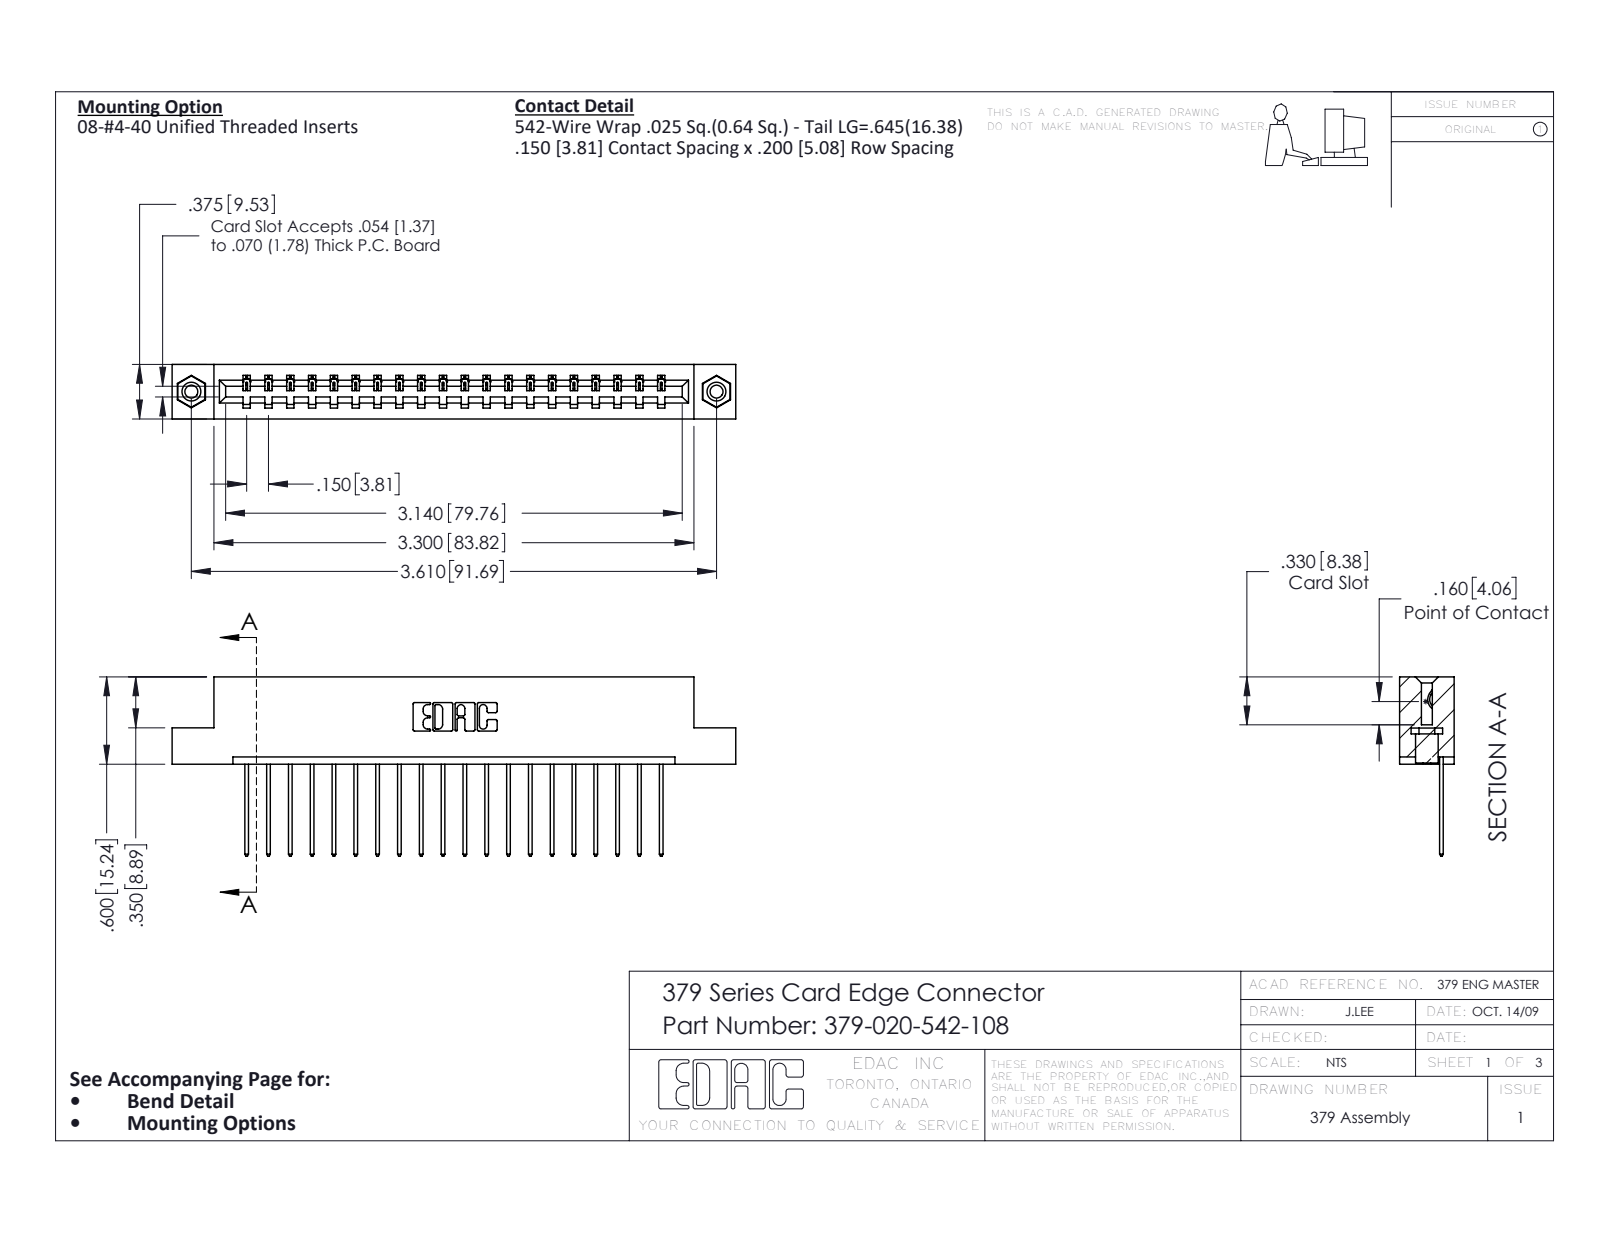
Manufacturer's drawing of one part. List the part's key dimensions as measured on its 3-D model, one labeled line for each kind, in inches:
Part name (STEP PRODUCT): 379 Part_Flush - .156 Dia - TI; 345-292-001_345-293-142; 345-250-001_345-250-003-102; 379-020-542-108
STEP written by: SolidWorks 2016 (CONFIG_CONTROL_DESIGN)
Units: inches
Bodies: 23 solids, 1334 faces (942 planar, 376 cylindrical, 16 other)
Overall size (bounding box): 3.875 × 1.232 × 0.375
Volume: 0.617 in³ · Surface area: 16.38 in²
Round holes (diameter × count): ⌀0.089 ×2, ⌀0.125 ×2, ⌀0.156 ×2
Round bosses / shafts (diameter × count): ⌀0.155 ×2
Partial cylindrical surfaces — rounded edges, fillets, slot ends (radius × count): R0.006 ×40, R0.01 ×40, R0.01 ×22, R0.007 ×6, R0.031 ×6, R0.026 ×3, R0.014 ×1, R0.022 ×1
Main face-to-face distances: 0.3, 0.075, 0.375, 0.6, 0.225, 0.15, 0.275, 0.2, 0.1, 0.025
Hole centre spacings: 3.61
